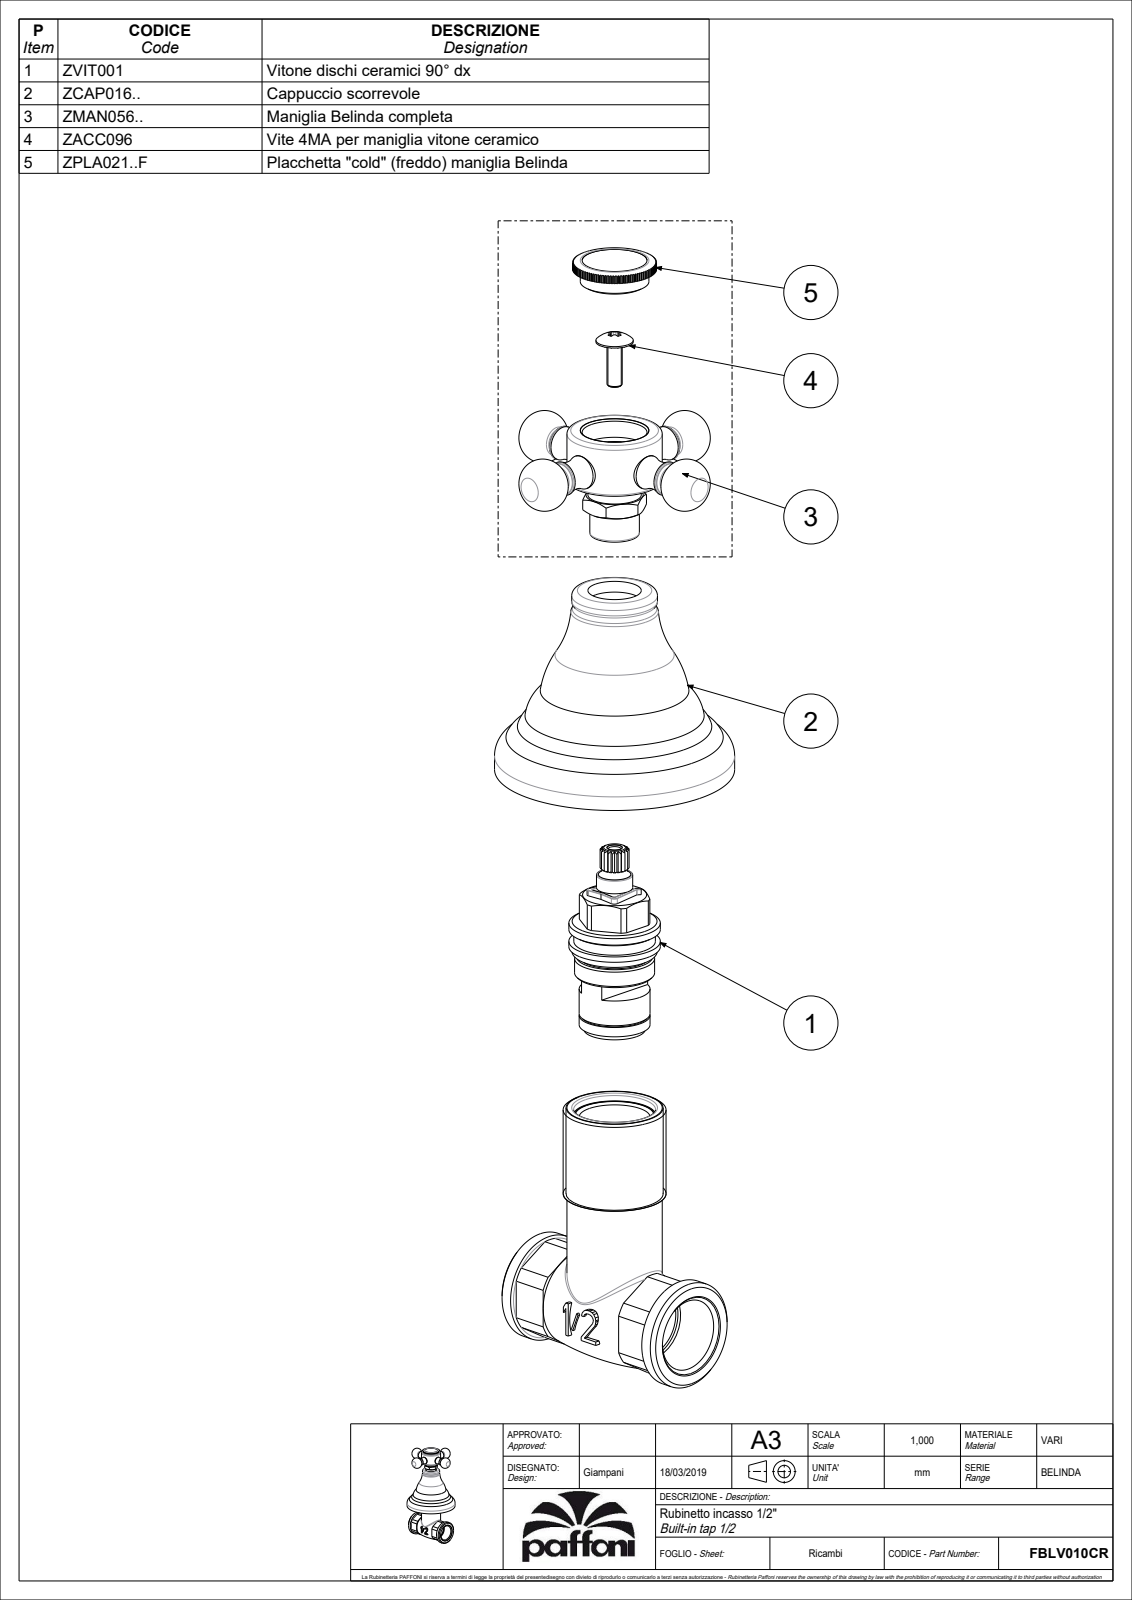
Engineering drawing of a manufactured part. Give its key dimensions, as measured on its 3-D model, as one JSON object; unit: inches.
{"part_name": "FBLV010CR", "step_written_by": "CREO PARAMETRIC BY PTC INC, 2020044 (CONFIG_CONTROL_DESIGN)", "units": "inches", "bodies": {"solids": 1, "faces": 441, "planar": 217, "cylindrical": 136, "other": 88}, "overall_size": [3.047, 2.522, 2.522], "volume_in3": 5.226, "surface_area_in2": 24.57, "round_bosses_or_shafts": [[0.354, 2], [0.276, 2], [2.48, 1], [0.984, 1], [0.886, 1], [0.551, 1], [0.512, 1]], "partial_cylinders_radius": [[0.433, 1]], "face_to_face_distances": [2.39, 1.969, 0.421, 0.591, 0.598, 0.157, 2.075, 0.106, 0.315, 2.941]}
